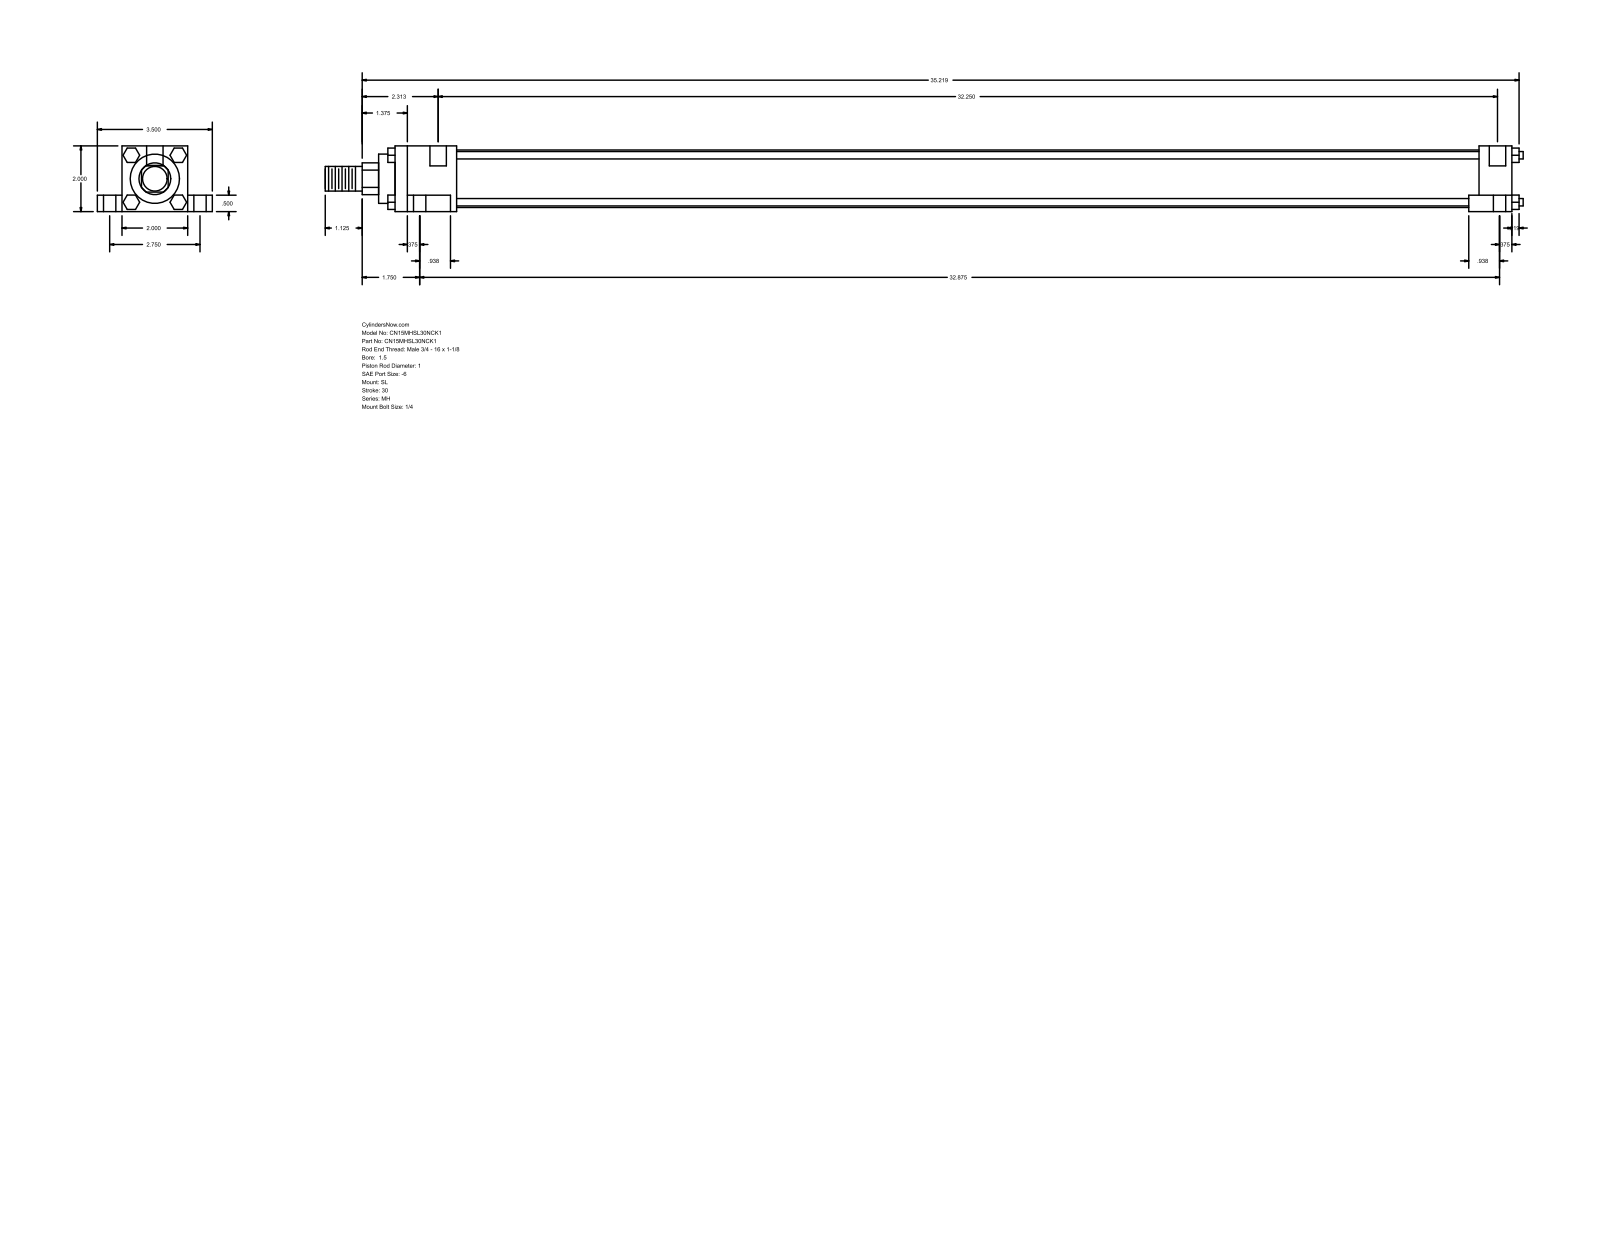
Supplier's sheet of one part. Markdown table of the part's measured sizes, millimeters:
| quantity | value |
| --- | --- |
| part name | MH_SL__0150_1 |
| STEP written by | GSSL Pune (CONFIG_CONTROL_DESIGN) |
| units | millimeters |
| bodies | 0 solids, 148 faces (112 planar, 36 cylindrical, 0 other) |
| overall size | 926.31 × 88.9 × 50.8 |
| round holes (diameter × count) | 5.56 × 4, 9.53 × 4, 15.88 × 4, 12.7 × 2 |
| round bosses / shafts (diameter × count) | 5.71 × 4, 44.45 × 1, 38.1 × 1, 25.4 × 1, 19.05 × 1 |
| partial cylindrical surfaces (radius × count) | 12.29 × 1 |
| main face-to-face distances | 50.8, 12.7, 38.1, 19.05, 69.85, 863.6, 25.4, 9.52, 33.34, 820.74 |
| hole center spacings | 34.96, 36.64, 37.73, 69.84, 821.48, 822.33, 824.66, 834.17 |
